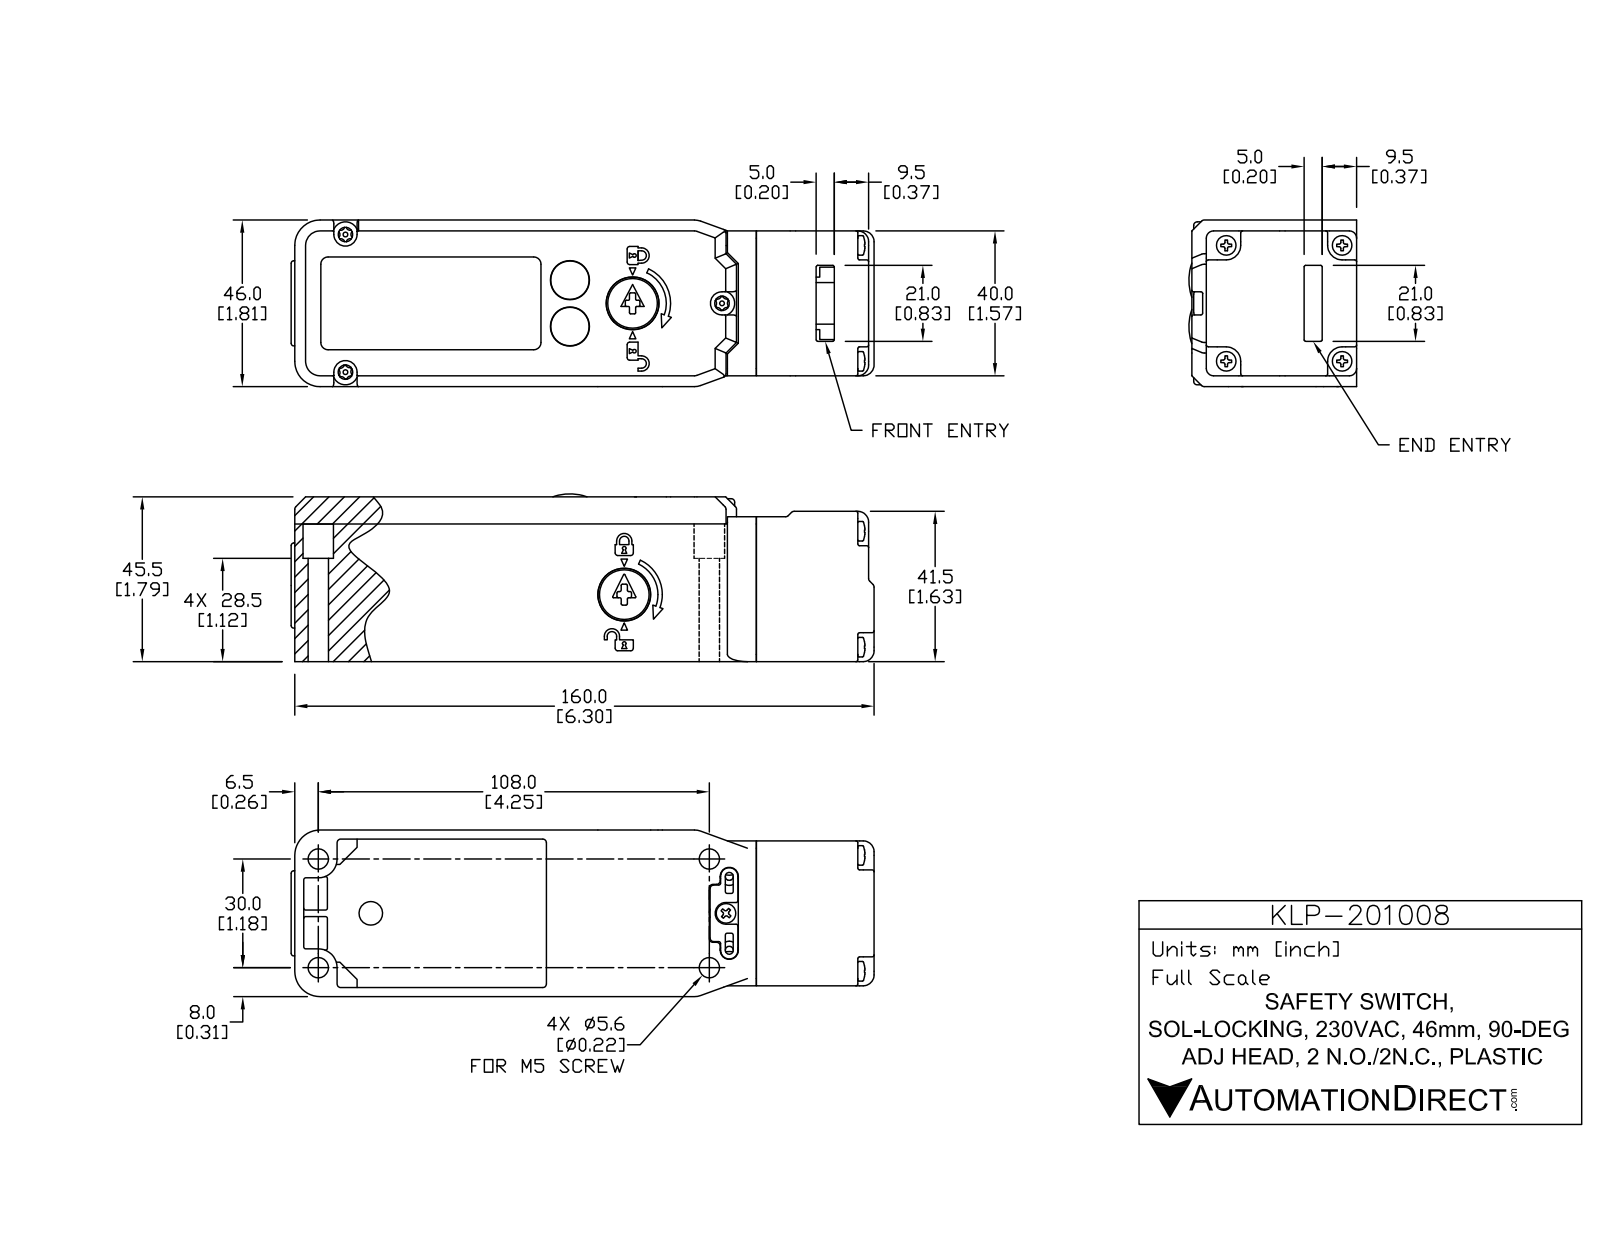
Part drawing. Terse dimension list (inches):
name: KLP-201008
written by: SolidWorks 2017 (AUTOMOTIVE_DESIGN)
unit: in
bodies: 8 solids, 476 faces (172 planar, 208 cylindrical, 96 other)
size: 6.339 × 1.823 × 1.811
volume: 18.35 in³; area: 79.89 in²
holes: 4× ⌀0.209, 4× ⌀0.386, 2× ⌀0.425, 1× ⌀0.276
bosses: 4× ⌀0.213, 3× ⌀0.051, 2× ⌀0.276, 1× ⌀0.925
rounds: 65× R0.02, 21× R0.039, 11× R0.079, 4× R0.118, 4× R0.157, 3× R0.098, 2× R0.045, 2× R0.197
face distances: 1.496, 1.811, 1.791, 0.295, 0.118, 1.693, 1.575, 0.374, 5.019, 5.02
hole spacings: 1.181, 1.553, 1.734, 2.757, 2.863, 4.252, 4.413, 0.335
